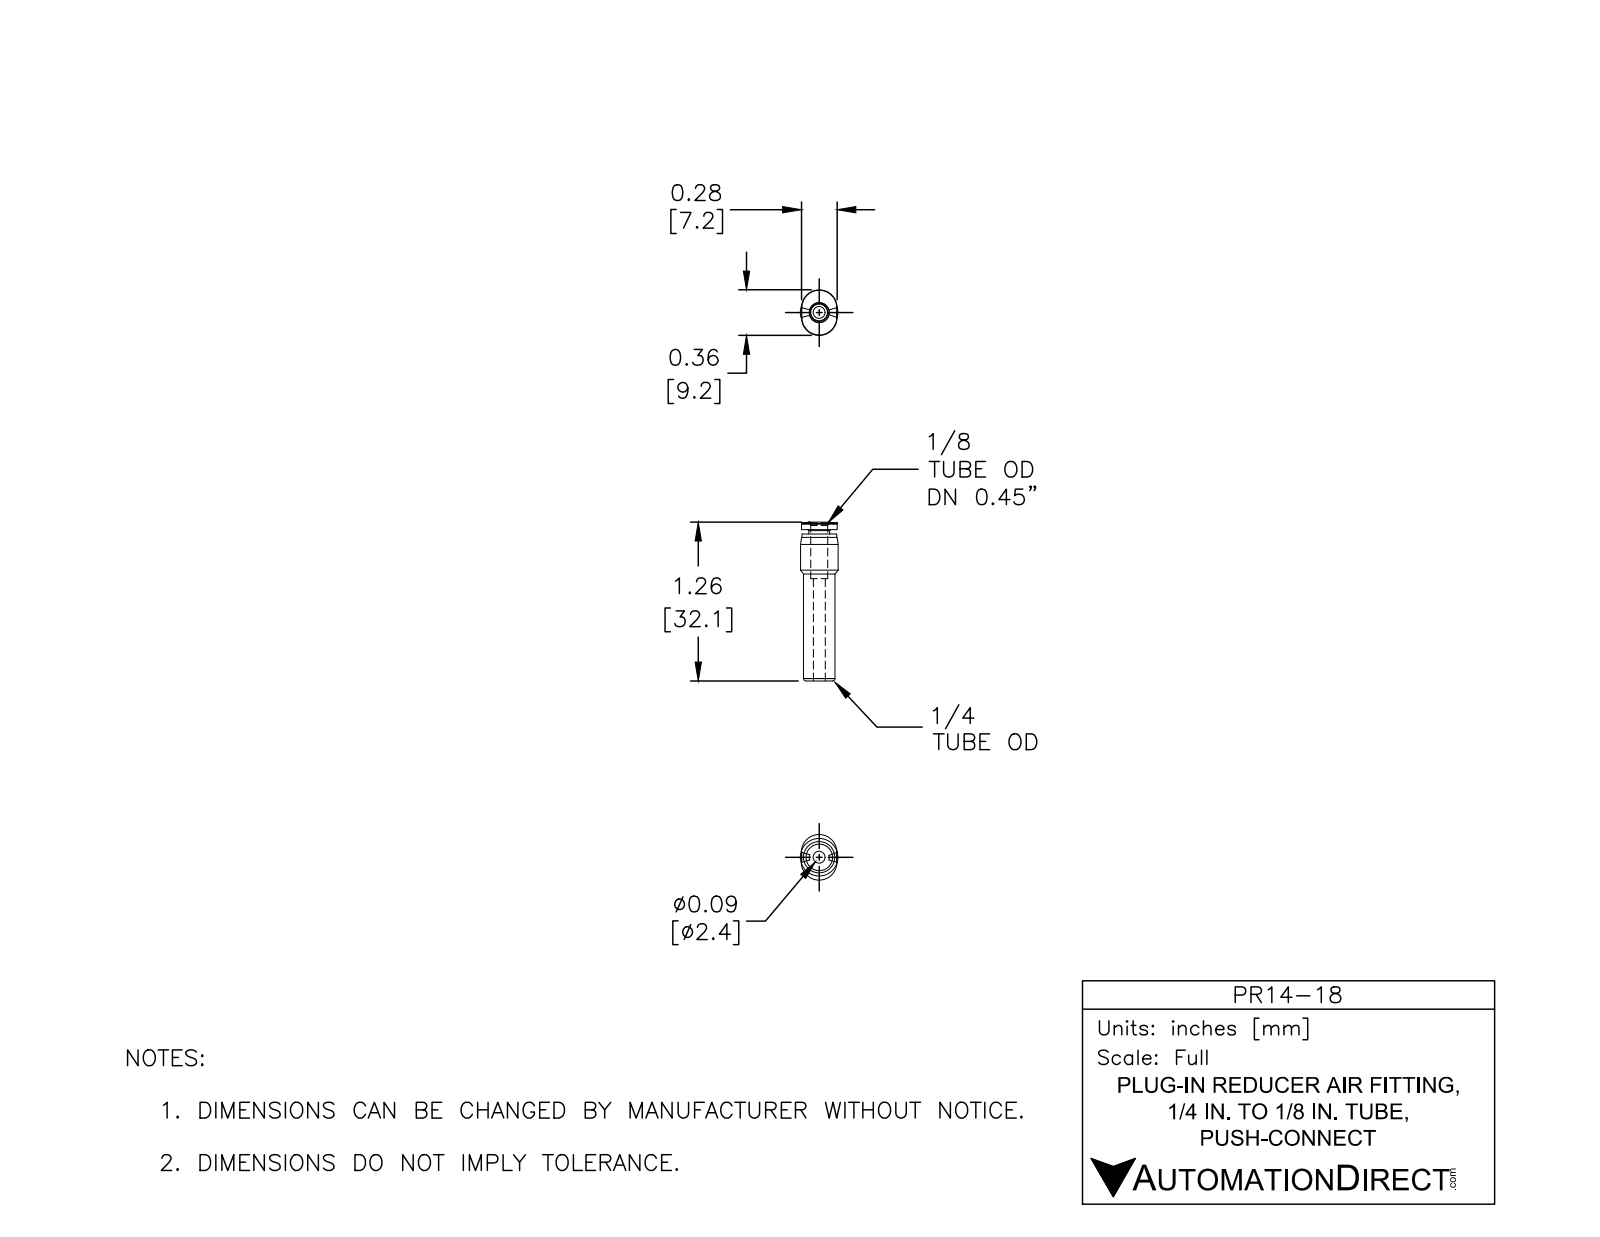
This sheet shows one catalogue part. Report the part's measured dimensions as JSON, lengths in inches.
{"part_name": "PR14-18", "step_written_by": "SolidWorks 2015 (CONFIG_CONTROL_DESIGN)", "units": "inches", "bodies": {"solids": 1, "faces": 47, "planar": 8, "cylindrical": 15, "other": 24}, "overall_size": [1.264, 0.362, 0.299], "volume_in3": 0.057, "surface_area_in2": 1.683, "round_holes": [[0.094, 1], [0.134, 1]], "round_bosses_or_shafts": [[0.299, 1], [0.276, 1], [0.25, 1], [0.165, 1]], "partial_cylinders_radius": [[0.142, 2]], "face_to_face_distances": [0.035, 1.169, 1.205, 0.815, 0.354, 0.39, 0.283, 1.142, 0.327, 0.028]}
